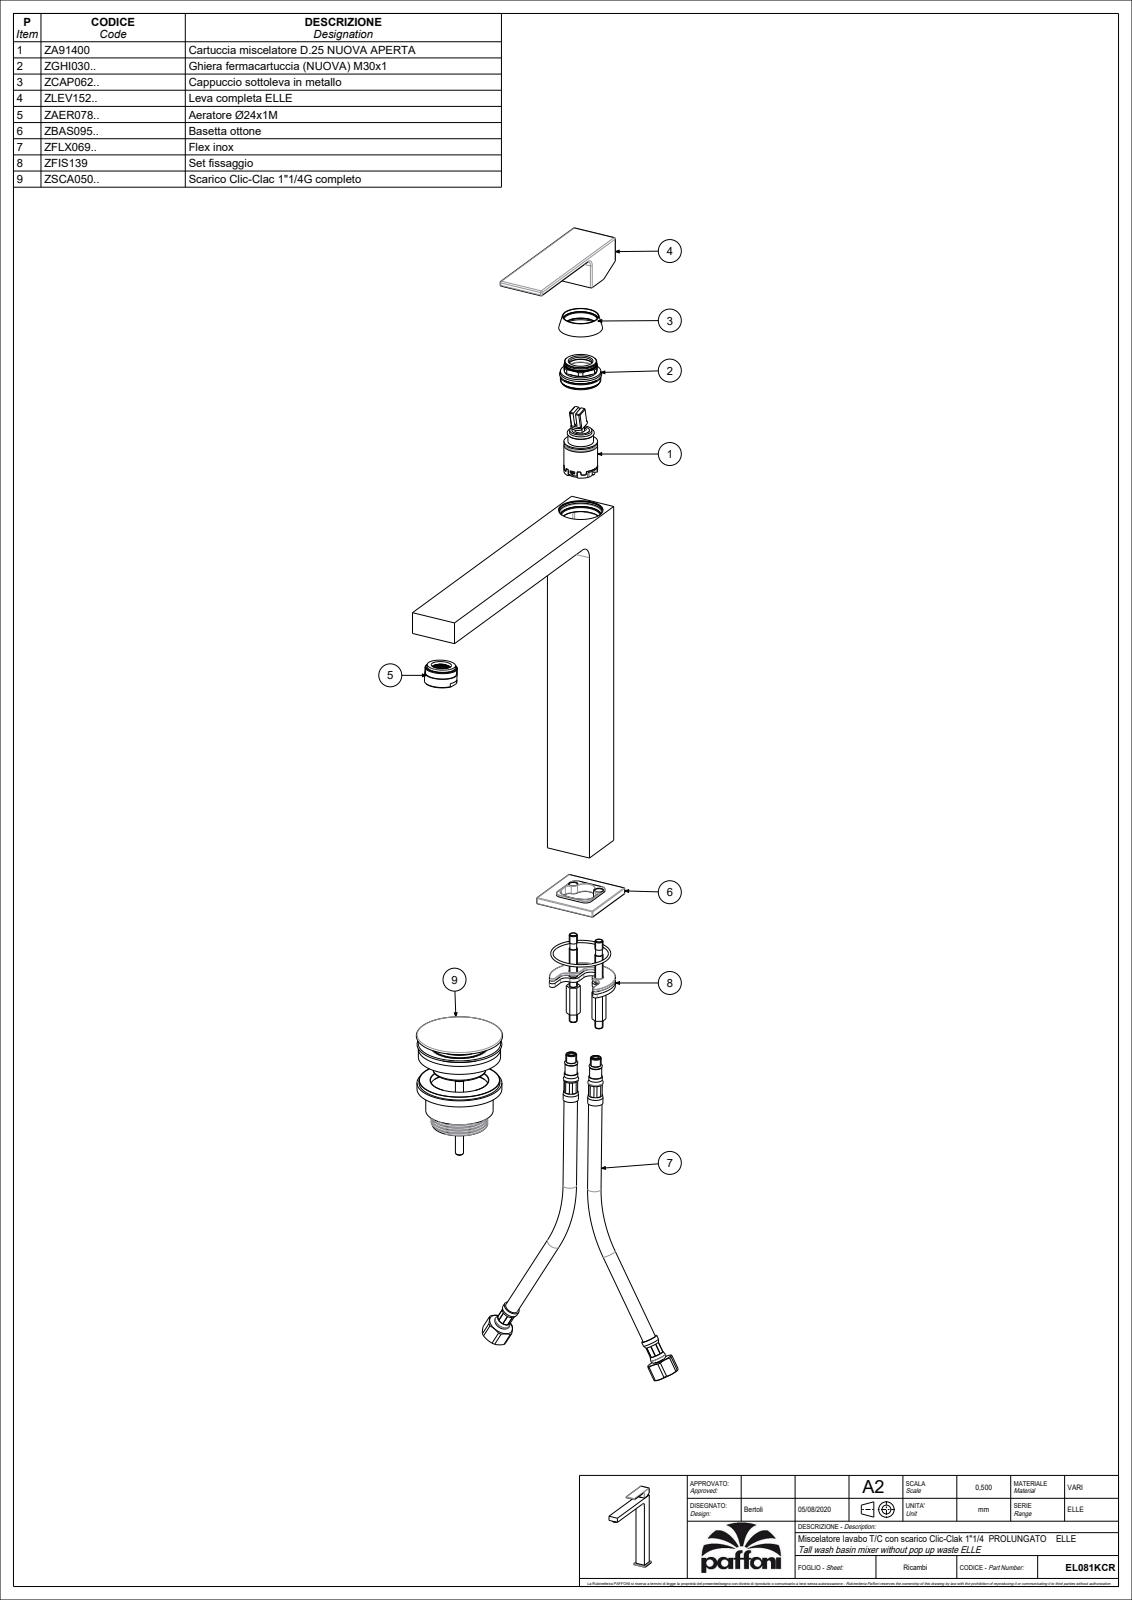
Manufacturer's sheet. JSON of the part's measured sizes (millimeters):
{"part_name": "EL081CR", "step_written_by": "CREO PARAMETRIC BY PTC INC, 2020044 (CONFIG_CONTROL_DESIGN)", "units": "millimeters", "bodies": {"solids": 2, "faces": 152, "planar": 55, "cylindrical": 57, "other": 40}, "overall_size": [306.78, 242.5, 48], "volume_mm3": 519041, "surface_area_mm2": 83272, "round_holes": [[3, 1], [4.5, 1], [5.5, 1], [24.8, 1], [26.2, 1], [28, 1]], "round_bosses_or_shafts": [[24, 1]], "partial_cylinders_radius": [[1, 13], [0.5, 12], [1.5, 8], [5, 1], [10.5, 1]], "face_to_face_distances": [36, 17, 45.28, 28.28, 41.28, 24.28, 4, 261.5, 278.5, 302.78]}
